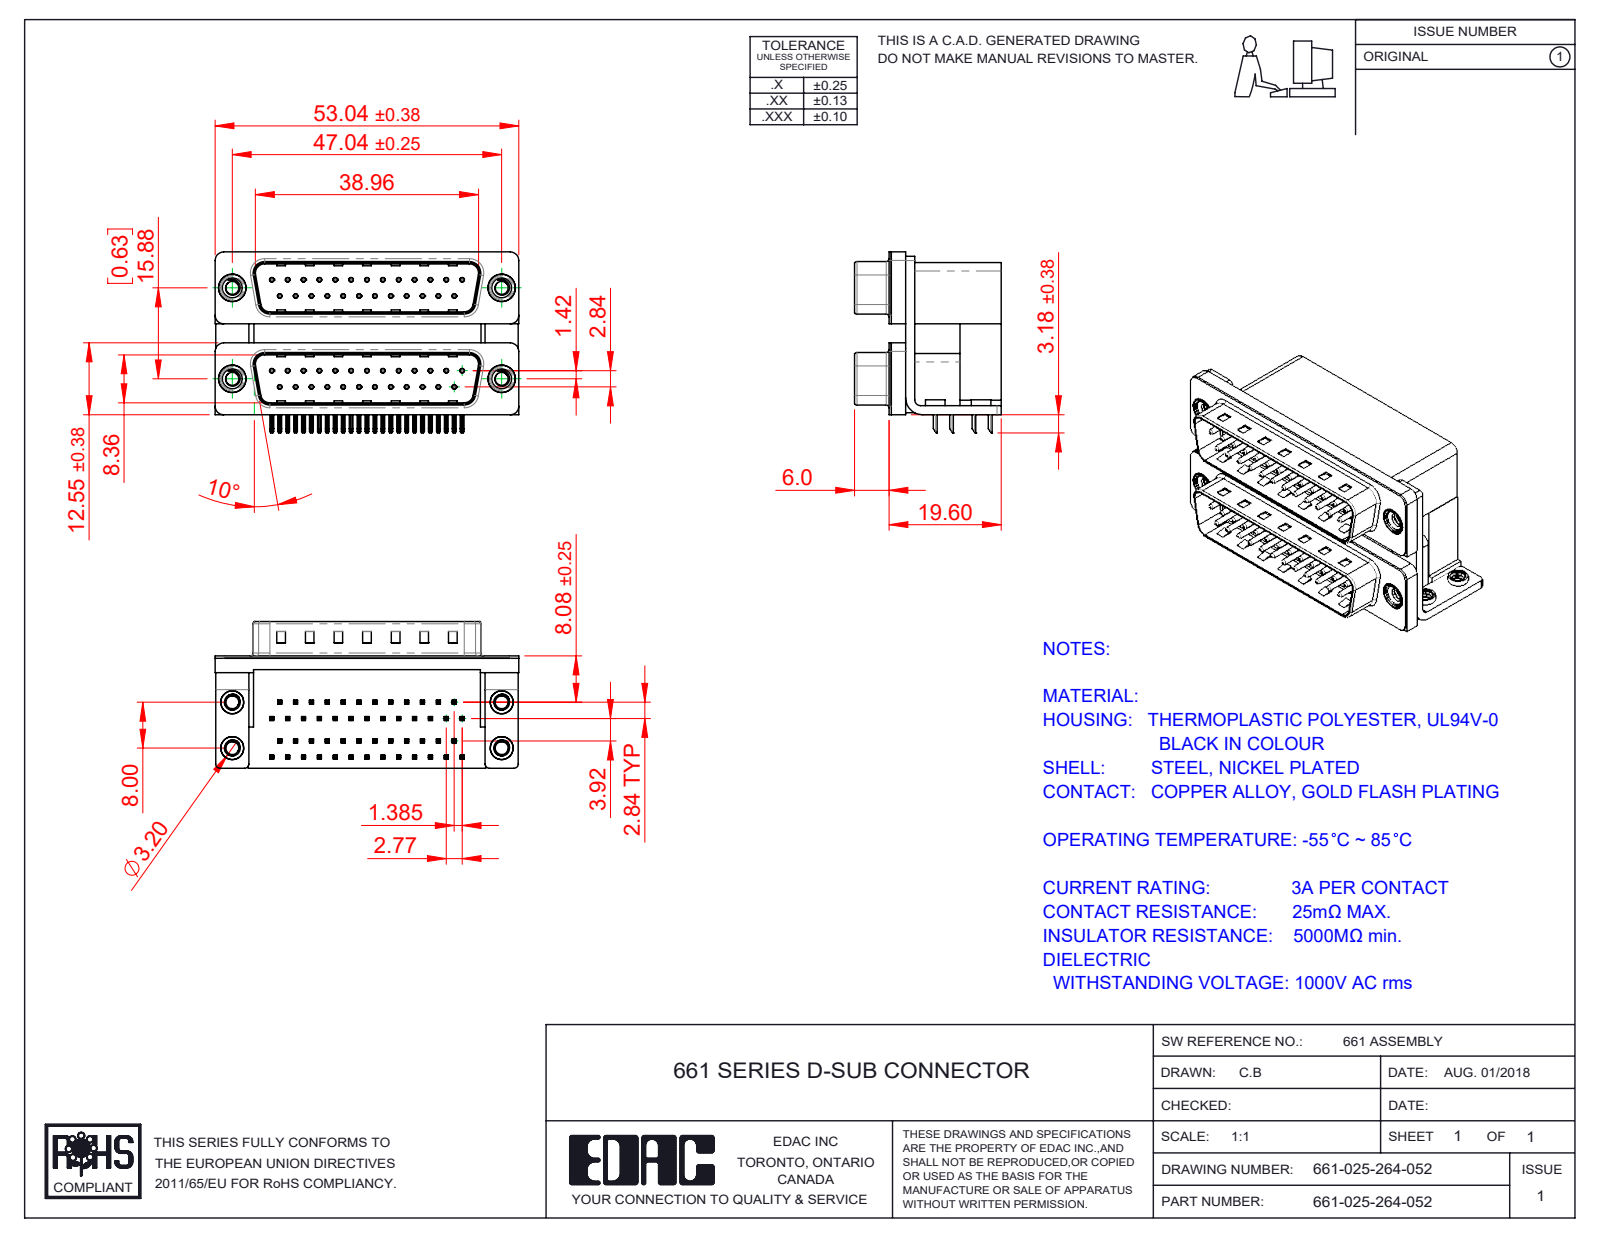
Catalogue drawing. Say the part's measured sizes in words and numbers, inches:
The part is named "661-025-264-052; 661 Contact Bottom Lower; 661 Housing Lower_25 Contacts; 661 Contact Top Upper_L (+8 more)". Its 3-D file was written by "SolidWorks 2020 (CONFIG_CONTROL_DESIGN)". It is 65 solids with 4754 faces: 2950 planar, 1358 cylindrical and 446 other. Overall it measures 2.088 by 1.244 by 1.008 inches. Its volume is 1.239 cubic inches and its surface area 33.31 square inches. Round holes: 50 of diameter 0.014, 50 of diameter 0.031, 8 of diameter 0.089, 4 of diameter 0.108, 4 of diameter 0.126, 4 of diameter 0.138, 4 of diameter 0.157, 4 of diameter 0.189, 4 of diameter 0.197. Round bosses or shafts: 50 of diameter 0.03, 4 of diameter 0.193, 4 of diameter 0.187, 4 of diameter 0.157, 4 of diameter 0.154, 4 of diameter 0.134. Partial cylindrical surfaces (rounded edges, fillets, slot ends): 200 of radius 0.01, 100 of radius 0.005, 16 of radius 0.02, 13 of radius 0.059, 8 of radius 0.03, 8 of radius 0.035, 8 of radius 0.063, 8 of radius 0.079. The main face-to-face distances are 0.016, 0.756, 0.283, 0.472, 0.421, 0.625, 0.657, 0.374, 0.098, 0.611. The hole center spacings are 0.124, 0.109, 0.218, 0.327, 0.436, 0.545, 0.654, 0.198.
